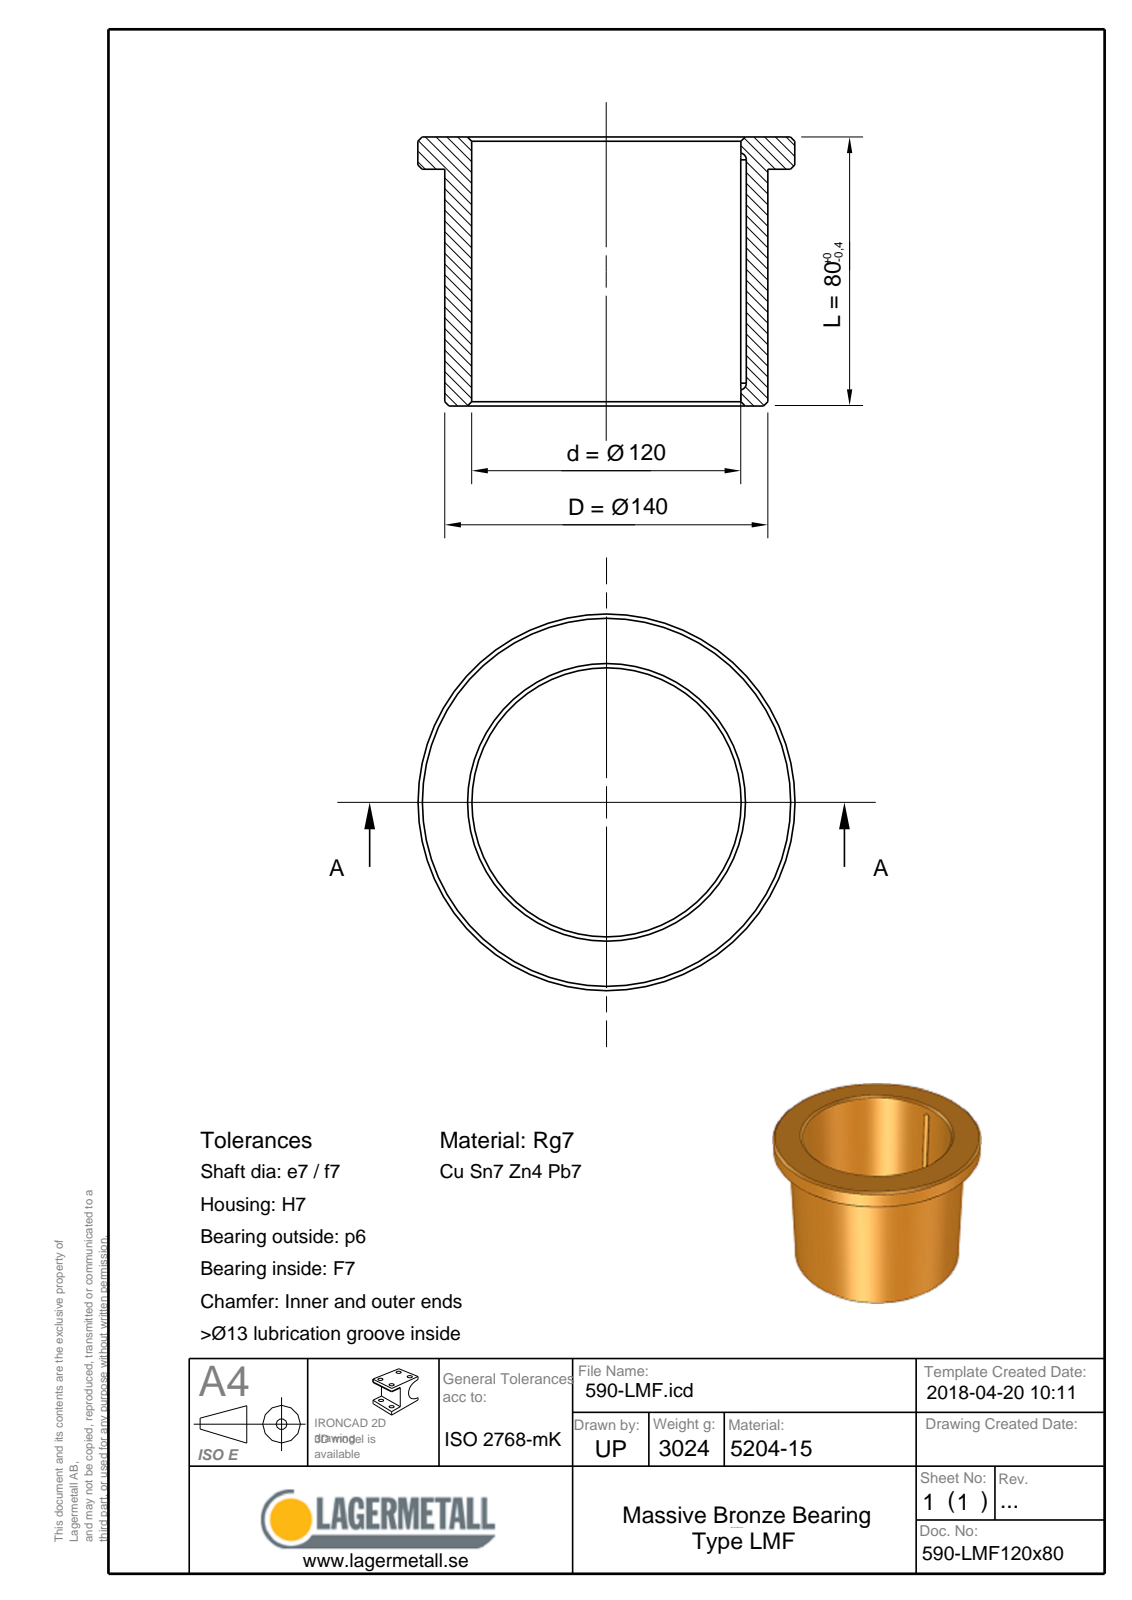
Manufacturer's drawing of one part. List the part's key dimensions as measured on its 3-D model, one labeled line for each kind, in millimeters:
Part name (STEP PRODUCT): 590-LMF120x80
STEP written by: Spatial InterOp 3D (CONFIG_CONTROL_DESIGN)
Units: millimetres
Bodies: 1 solid, 16 faces (4 planar, 5 cylindrical, 7 other)
Overall size (bounding box): 150 × 150 × 80
Volume: 343 596 mm³ · Surface area: 77 182 mm²
Round holes (diameter × count): ⌀120 ×1
Round bosses / shafts (diameter × count): ⌀150 ×1, ⌀140 ×1
Partial cylindrical surfaces — rounded edges, fillets, slot ends (radius × count): R1.75 ×2
Main face-to-face distances: 80, 72, 8
